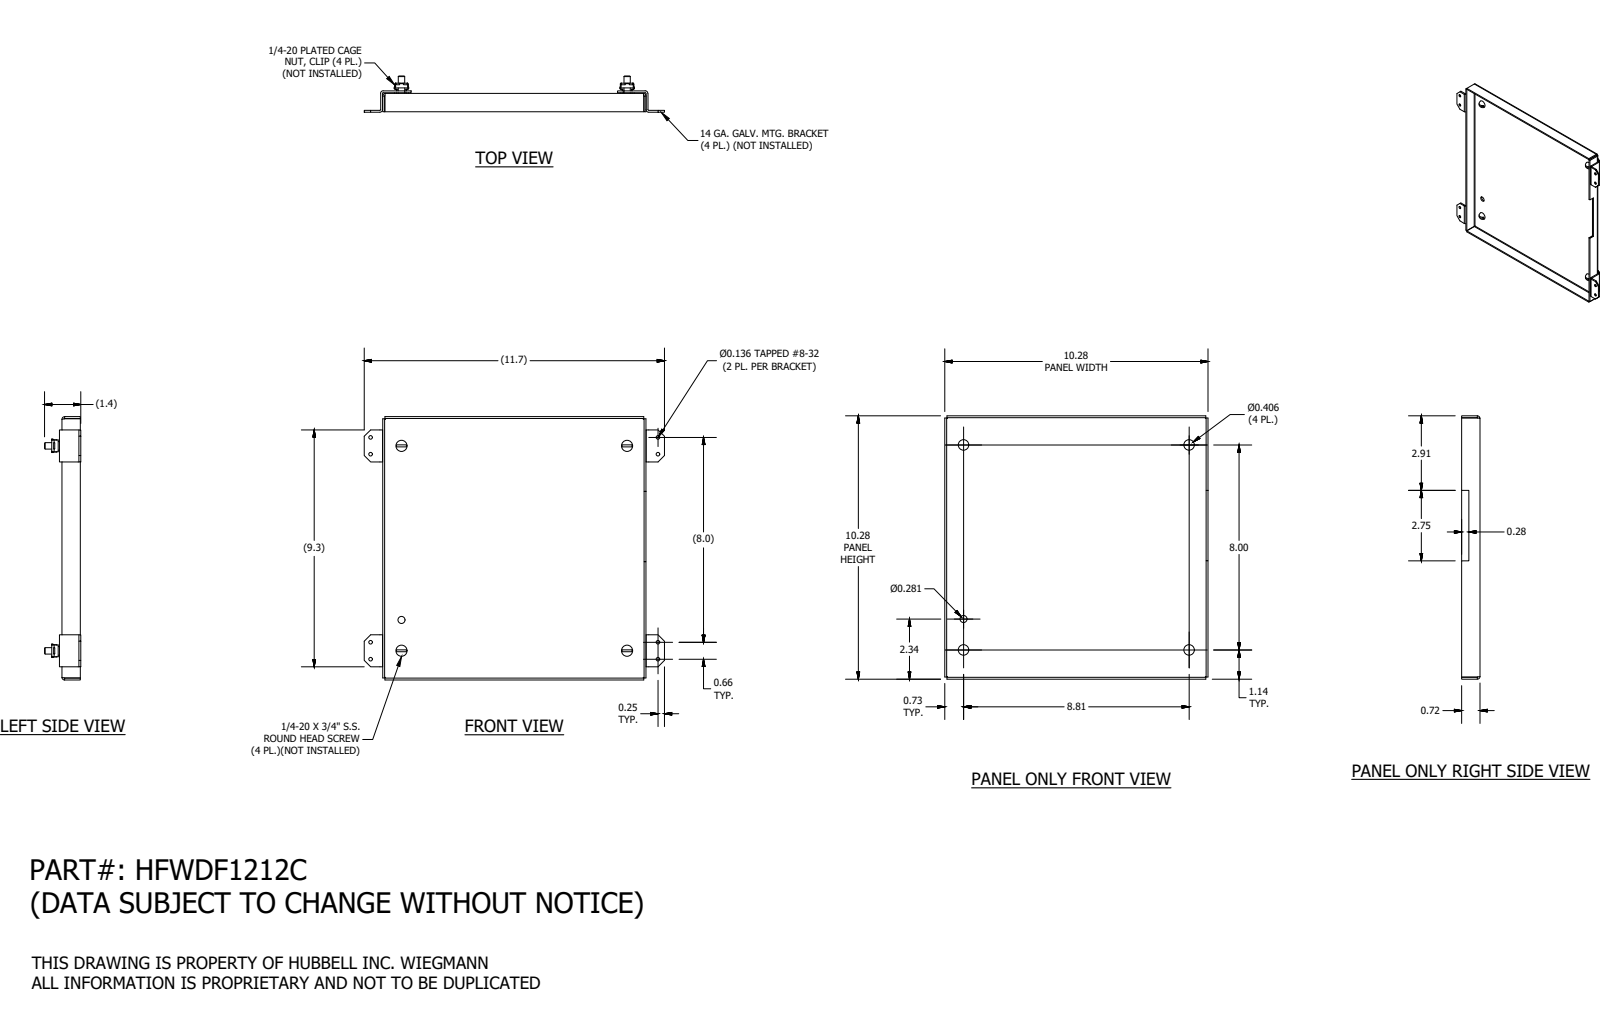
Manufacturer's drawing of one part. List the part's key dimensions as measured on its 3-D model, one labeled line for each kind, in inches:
Part name (STEP PRODUCT): HFWDF1212C
STEP written by: SolidWorks 2023 (AUTOMOTIVE_DESIGN)
Units: inches
Bodies: 13 solids, 595 faces (418 planar, 161 cylindrical, 16 other)
Overall size (bounding box): 11.726 × 10.281 × 1.415
Volume: 10.8 in³ · Surface area: 299.8 in²
Round holes (diameter × count): ⌀0.136 ×8, ⌀0.185 ×4, ⌀0.328 ×4, ⌀0.406 ×4, ⌀0.281 ×1
Round bosses / shafts (diameter × count): ⌀0.25 ×4
Partial cylindrical surfaces — rounded edges, fillets, slot ends (radius × count): R0.025 ×20, R0.021 ×16, R0.045 ×12, R0.031 ×8, R0.105 ×8, R0.021 ×4
Main face-to-face distances: 0.074, 10.207, 10.133, 10.281, 0.094, 0.078, 10.285, 0.759, 0.665, 0.02
Hole centre spacings: 1.251, 10.025, 8, 0.66, 7.765, 8.417, 11.227, 11.246
